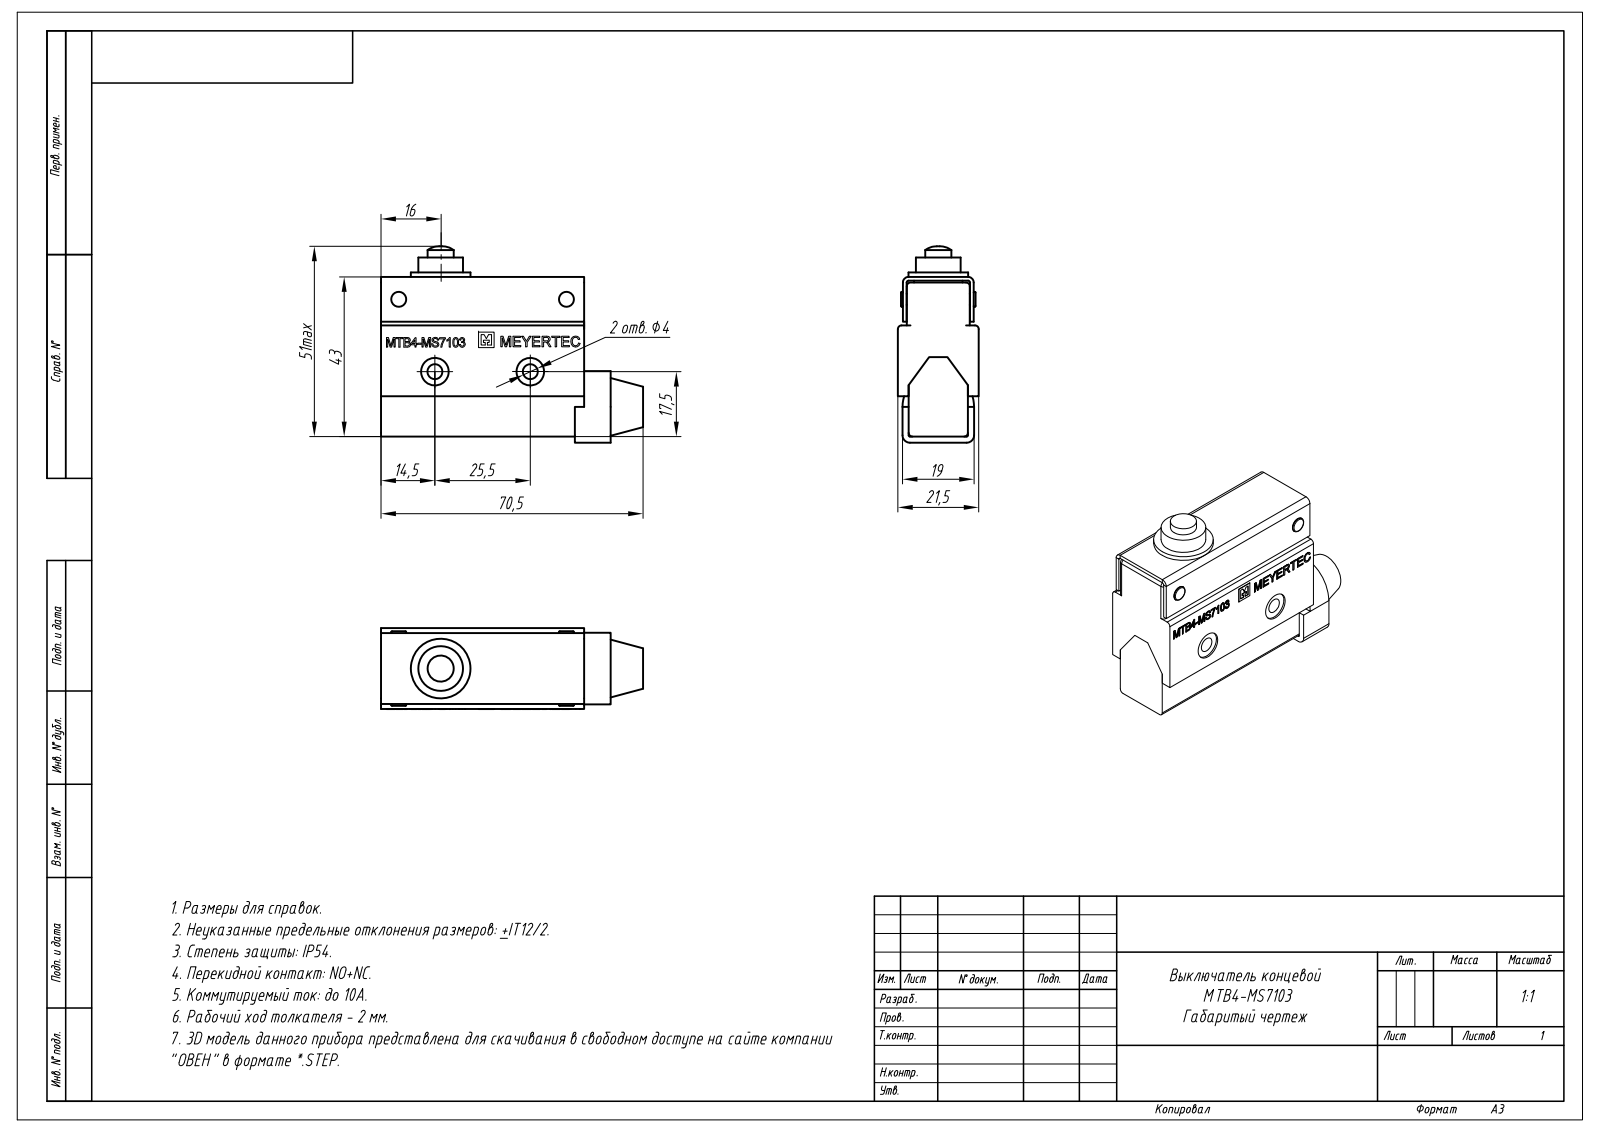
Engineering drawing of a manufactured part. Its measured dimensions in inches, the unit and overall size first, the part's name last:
Units: inches
Overall size (bounding box): 2.795 × 2.075 × 0.866
Round holes (diameter × count): ⌀0.166 ×2
Round bosses / shafts (diameter × count): ⌀0.551 ×1, ⌀0.472 ×1, ⌀0.276 ×1
Partial cylindrical surfaces — rounded edges, fillets, slot ends (radius × count): R0.039 ×12, R0.098 ×2, R0.386 ×1
Main face-to-face distances: 0.059, 0.748, 0.807, 0.118, 0.689, 0.866, 1.673, 0.63, 2.146, 0.453
Hole centre spacings: 1.004
Volume: 2.994 in³ · Surface area: 15.88 in²
Bodies: 1 solid, 51 faces (26 planar, 20 cylindrical, 5 other)
Part name (STEP PRODUCT): MTB4-MS7103
STEP written by: C3D Toolkit (CONFIG_CONTROL_DESIGN)
